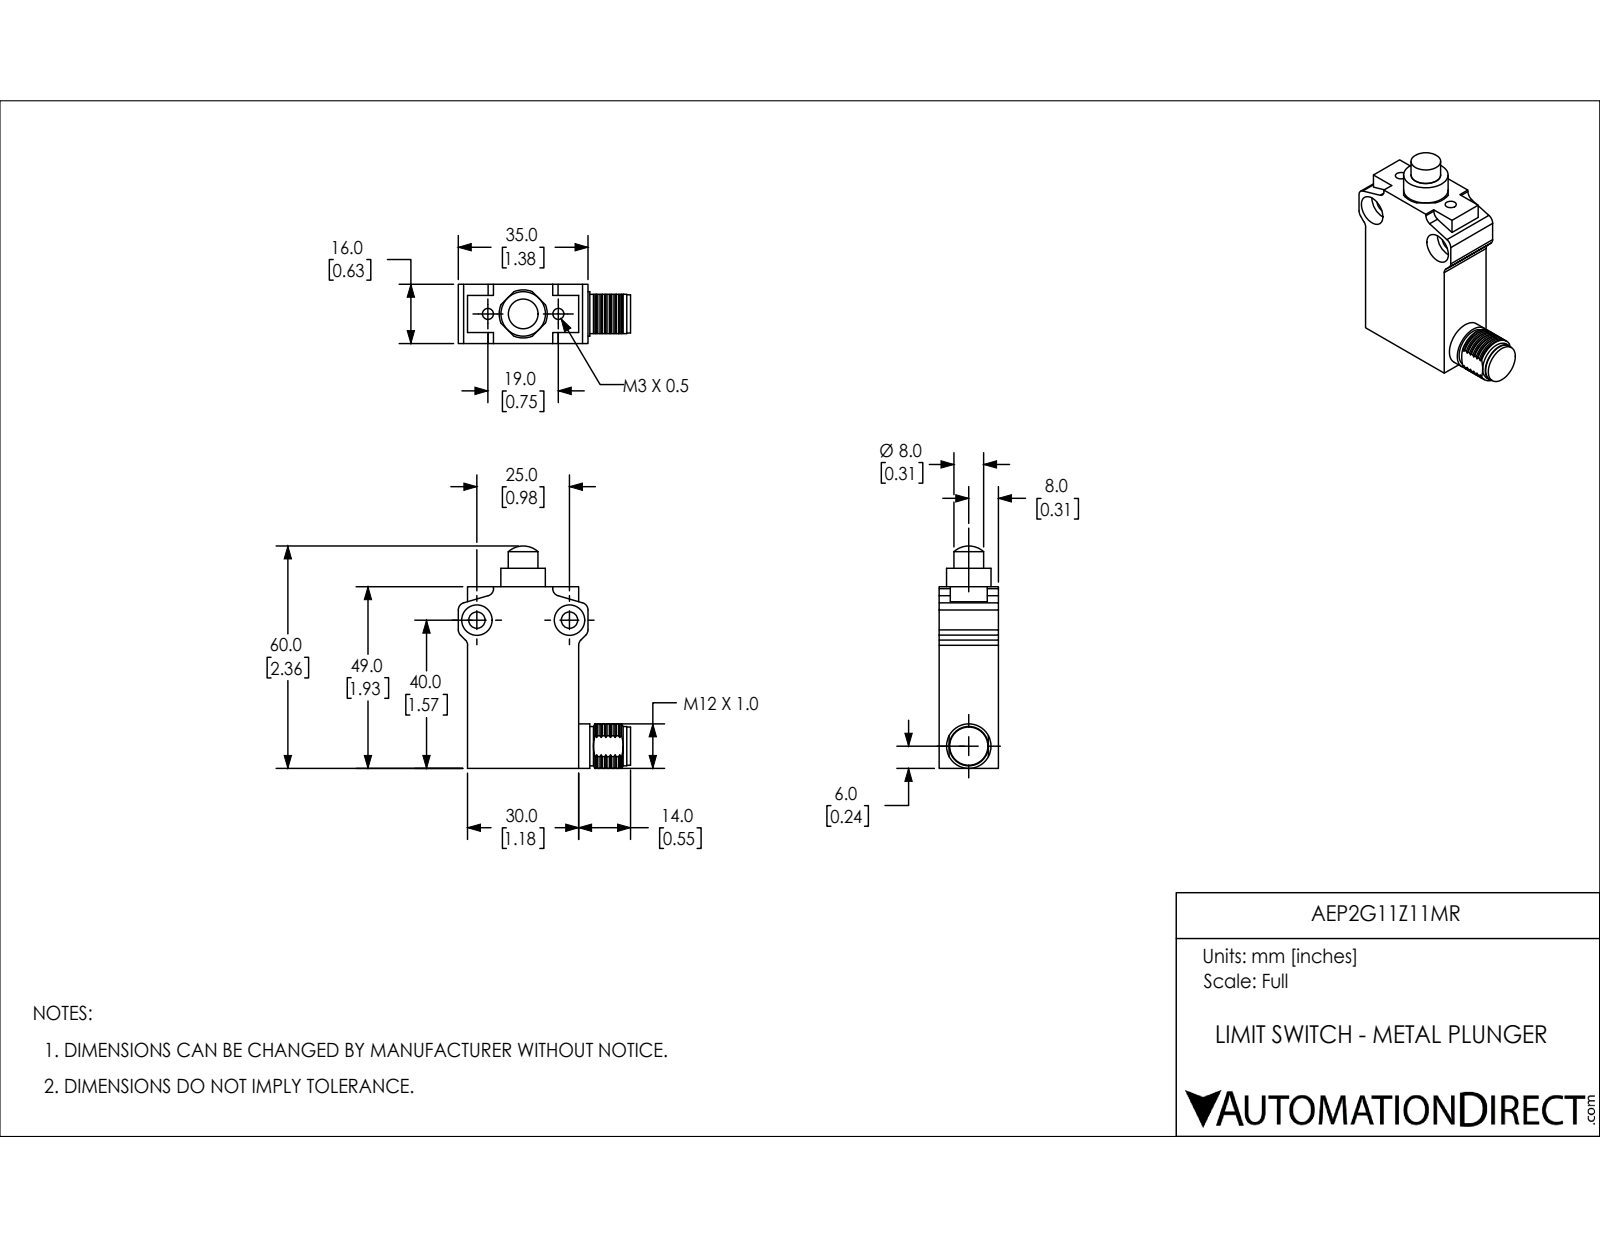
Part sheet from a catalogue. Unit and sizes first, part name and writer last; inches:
Units: inches
Overall size (bounding box): 2.362 × 1.831 × 0.63
Round holes (diameter × count): ⌀0.118 ×2, ⌀0.173 ×2, ⌀0.323 ×2, ⌀0.315 ×1
Round bosses / shafts (diameter × count): ⌀0.472 ×2, ⌀0.417 ×1, ⌀0.406 ×1
Partial cylindrical surfaces — rounded edges, fillets, slot ends (radius × count): R0.079 ×8, R0.256 ×1
Main face-to-face distances: 0.63, 1.181, 1.929, 0.472, 0.098, 1.28, 0.157, 1.74, 0.189, 2.126
Hole centre spacings: 0.374, 0.748, 0.984
Volume: 1.481 in³ · Surface area: 12.22 in²
Bodies: 4 solids, 164 faces (42 planar, 79 cylindrical, 43 other)
Part name (STEP PRODUCT): AEP2G11Z11MR
STEP written by: SolidWorks 2018 (AUTOMOTIVE_DESIGN)
